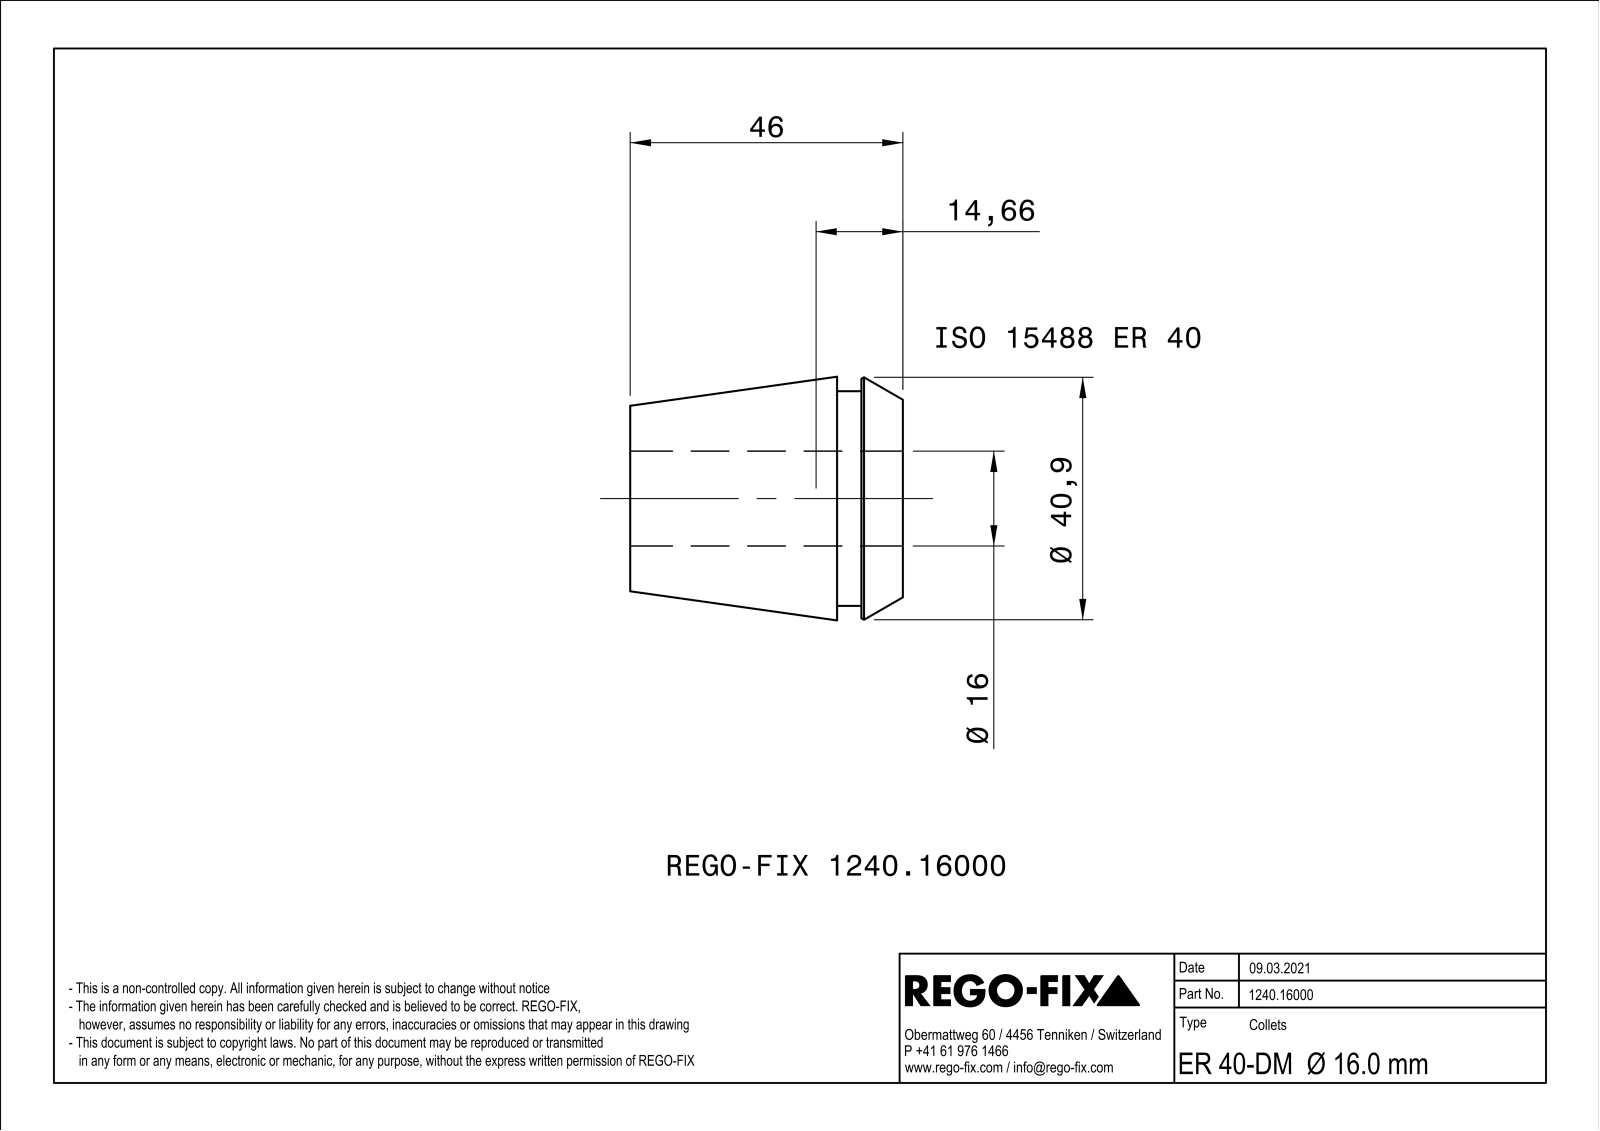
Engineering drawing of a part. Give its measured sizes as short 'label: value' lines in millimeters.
name: NOCUT
written by: SIEMENS PLM Software Solid Edge ST10 (AUTOMOTIVE_DESIGN)
unit: mm
bodies: 1 solid, 154 faces (80 planar, 9 cylindrical, 65 other)
size: 46 × 40.99 × 40.99
volume: 32 936 mm³; area: 19 628 mm²
holes: 1× ⌀16
bosses: 1× ⌀36.2
face distances: 1, 46, 11.1, 34.9, 7, 4.1, 39, 17, 10, 5.9
